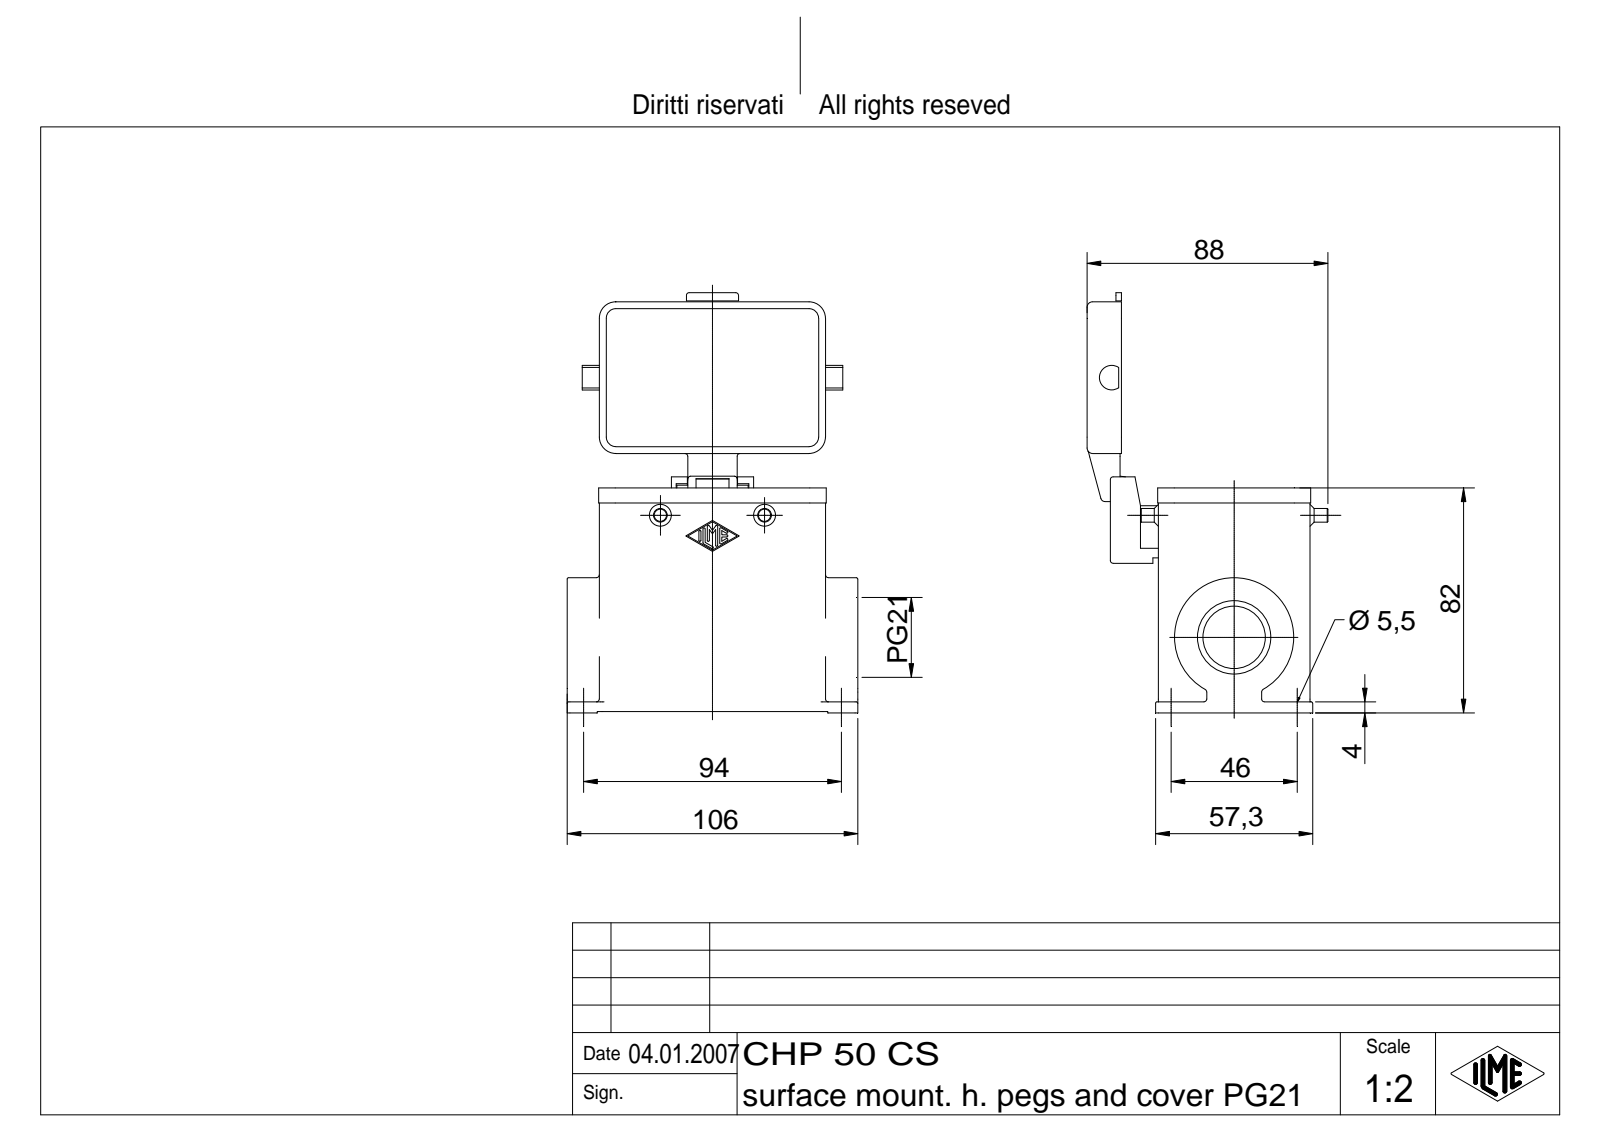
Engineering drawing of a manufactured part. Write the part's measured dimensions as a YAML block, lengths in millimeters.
part_name: "CHP 50 CS"
step_written_by: "Autodesk Inventor 7 (AUTOMOTIVE_DESIGN)"
units: millimeters
bodies: {solids: 3, faces: 609, planar: 180, cylindrical: 239, other: 190}
overall_size: [153.15, 106, 87.8]
volume: 173084
surface_area: 80463
round_holes:
  - {diameter: 2.46, count: 4}
  - {diameter: 3.1, count: 4}
  - {diameter: 5.5, count: 2}
  - {diameter: 4, count: 1}
  - {diameter: 22.78, count: 1}
  - {diameter: 26.78, count: 1}
round_bosses_or_shafts:
  - {diameter: 5, count: 3}
  - {diameter: 3, count: 2}
  - {diameter: 43.5, count: 1}
  - {diameter: 7, count: 1}
  - {diameter: 4, count: 1}
partial_cylinders:
  - {radius: 1, count: 38}
  - {radius: 0.5, count: 17}
  - {radius: 0.38, count: 14}
  - {radius: 6, count: 12}
  - {radius: 2, count: 8}
  - {radius: 1.5, count: 5}
  - {radius: 3, count: 4}
  - {radius: 3.5, count: 4}
face_to_face_distances: [3, 52.3, 3.5, 55.3, 22.5, 49.3, 26, 81.3, 78.3, 29]
hole_center_spacings: [16, 66, 67.91, 14.32, 23.6, 30.41, 45.22, 80.06]
